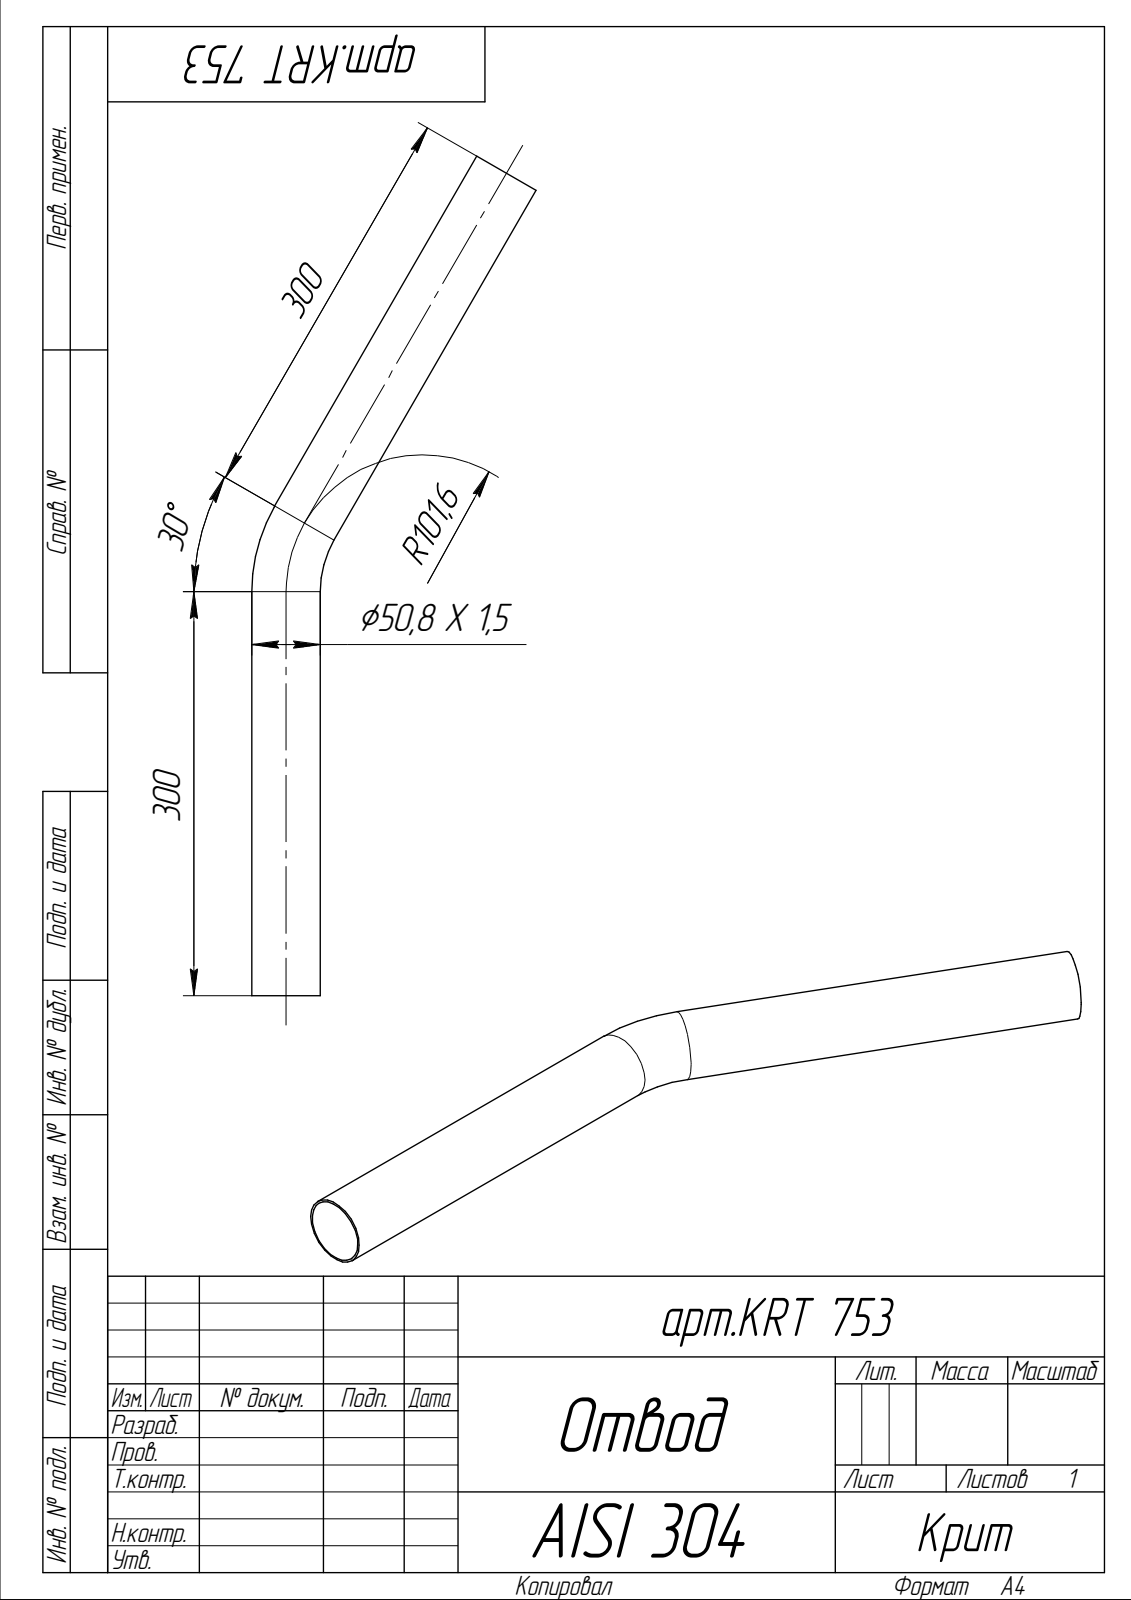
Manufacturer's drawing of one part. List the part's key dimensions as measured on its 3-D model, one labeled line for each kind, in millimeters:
Part name (STEP PRODUCT): Деталь
STEP written by: ASCON Math Kernel (AUTOMOTIVE_DESIGN)
Units: millimetres
Bodies: 1 solid, 8 faces (2 planar, 4 cylindrical, 2 other)
Overall size (bounding box): 623.31 × 211.01 × 50.8
Volume: 151 751 mm³ · Surface area: 202 800 mm²
Round holes (diameter × count): ⌀47.8 ×2
Round bosses / shafts (diameter × count): ⌀50.8 ×2
